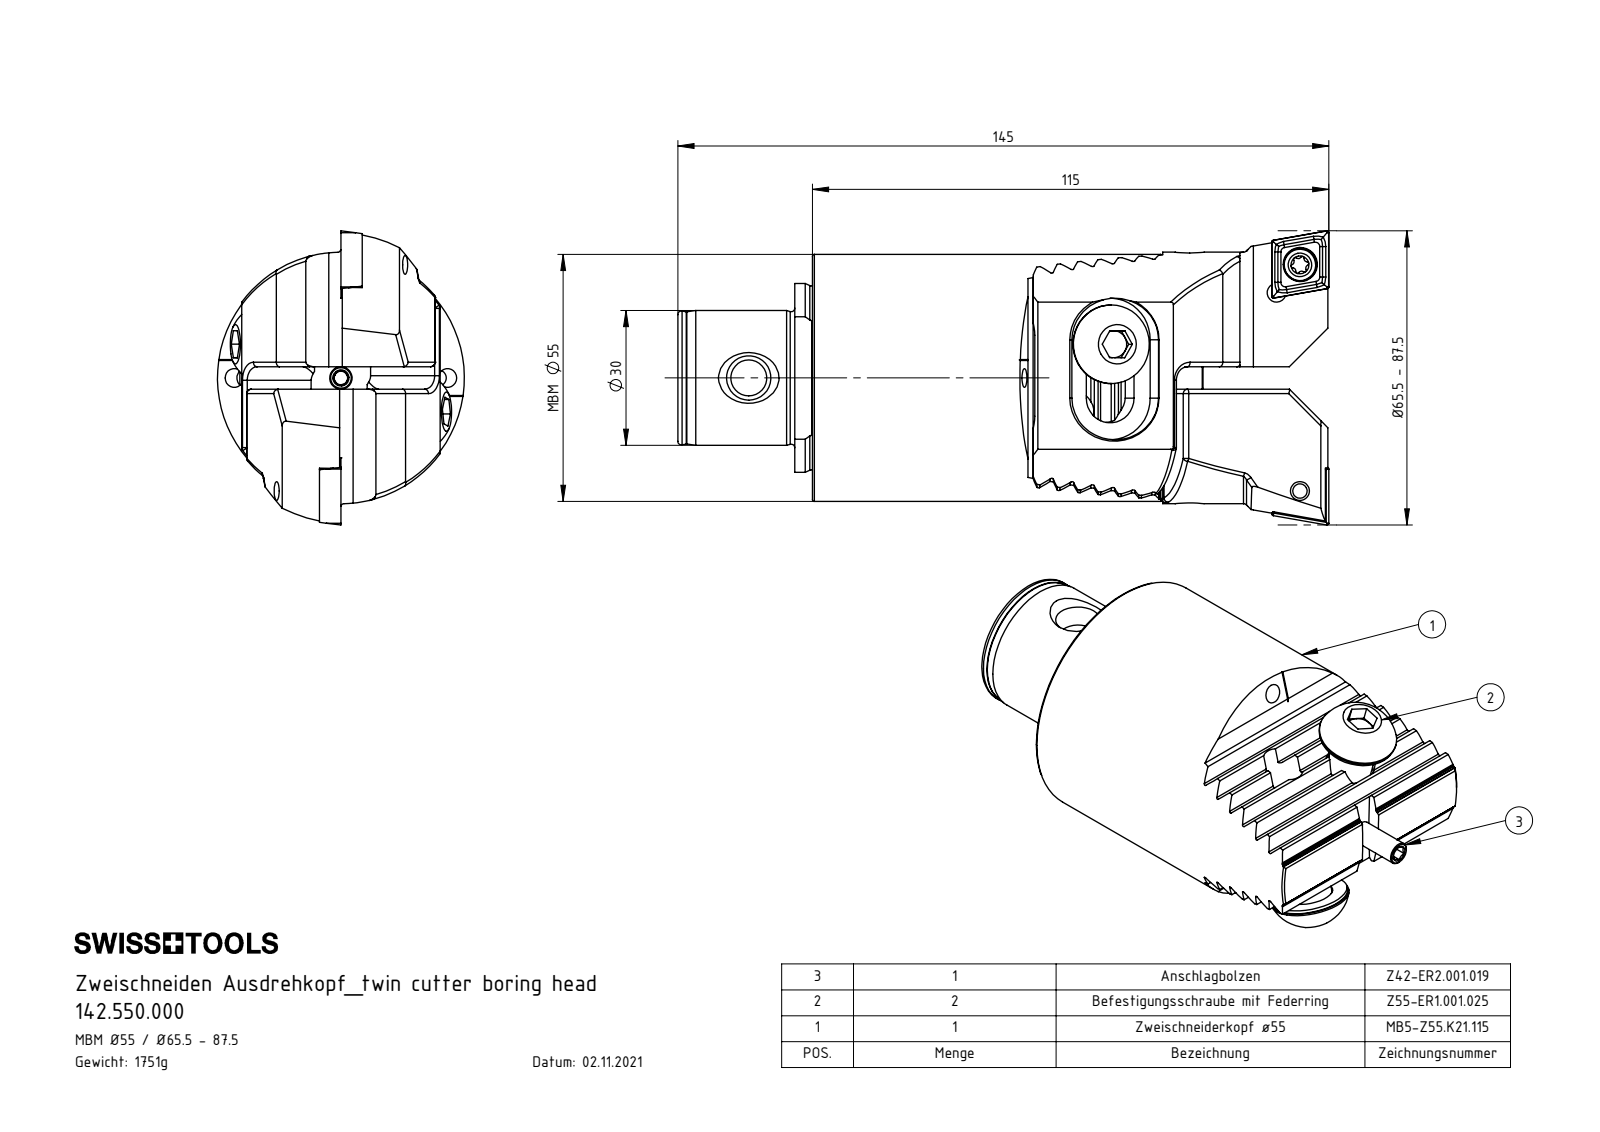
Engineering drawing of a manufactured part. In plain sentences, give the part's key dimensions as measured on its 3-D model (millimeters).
The part is named "142.550.000; Z42-ER2.001.019_A; Z55-ER1.001.025; Z55-ER1.003.025_A_gespannt (+7 more)". Its 3-D file was written by "SolidWorks 2017 (CONFIG_CONTROL_DESIGN)". It is 14 solids with 1024 faces: 490 planar, 223 cylindrical and 311 other. Overall it measures 145 by 65.5 by 55 millimeters. Its volume is 223 832 cubic millimeters and its surface area 53 154 square millimeters. Round holes: 7 of diameter 4.2, 2 of diameter 2, 2 of diameter 5.5, 2 of diameter 7.6, 2 of diameter 8.5, 2 of diameter 10.5, 2 of diameter 11, 1 of diameter 3, 1 of diameter 3.3, 1 of diameter 5, 1 of diameter 8, 1 of diameter 14. Round bosses or shafts: 3 of diameter 5, 2 of diameter 17.5, 2 of diameter 17, 2 of diameter 10, 2 of diameter 7, 2 of diameter 4, 1 of diameter 55, 1 of diameter 30. Partial cylindrical surfaces (rounded edges, fillets, slot ends): 14 of radius 0.34, 14 of radius 1, 12 of radius 0.34, 12 of radius 0.39, 12 of radius 0.69, 6 of radius 3, 4 of radius 5.5, 4 of radius 9.25. The main face-to-face distances are 4.07, 8.14, 12.21, 16.28, 4.11, 20.35, 4.03, 4.01, 8.18, 4.13. The hole center spacings are 8.08, 8.2, 16, 44.46, 44.55, 50.43, 70, 76.82.
